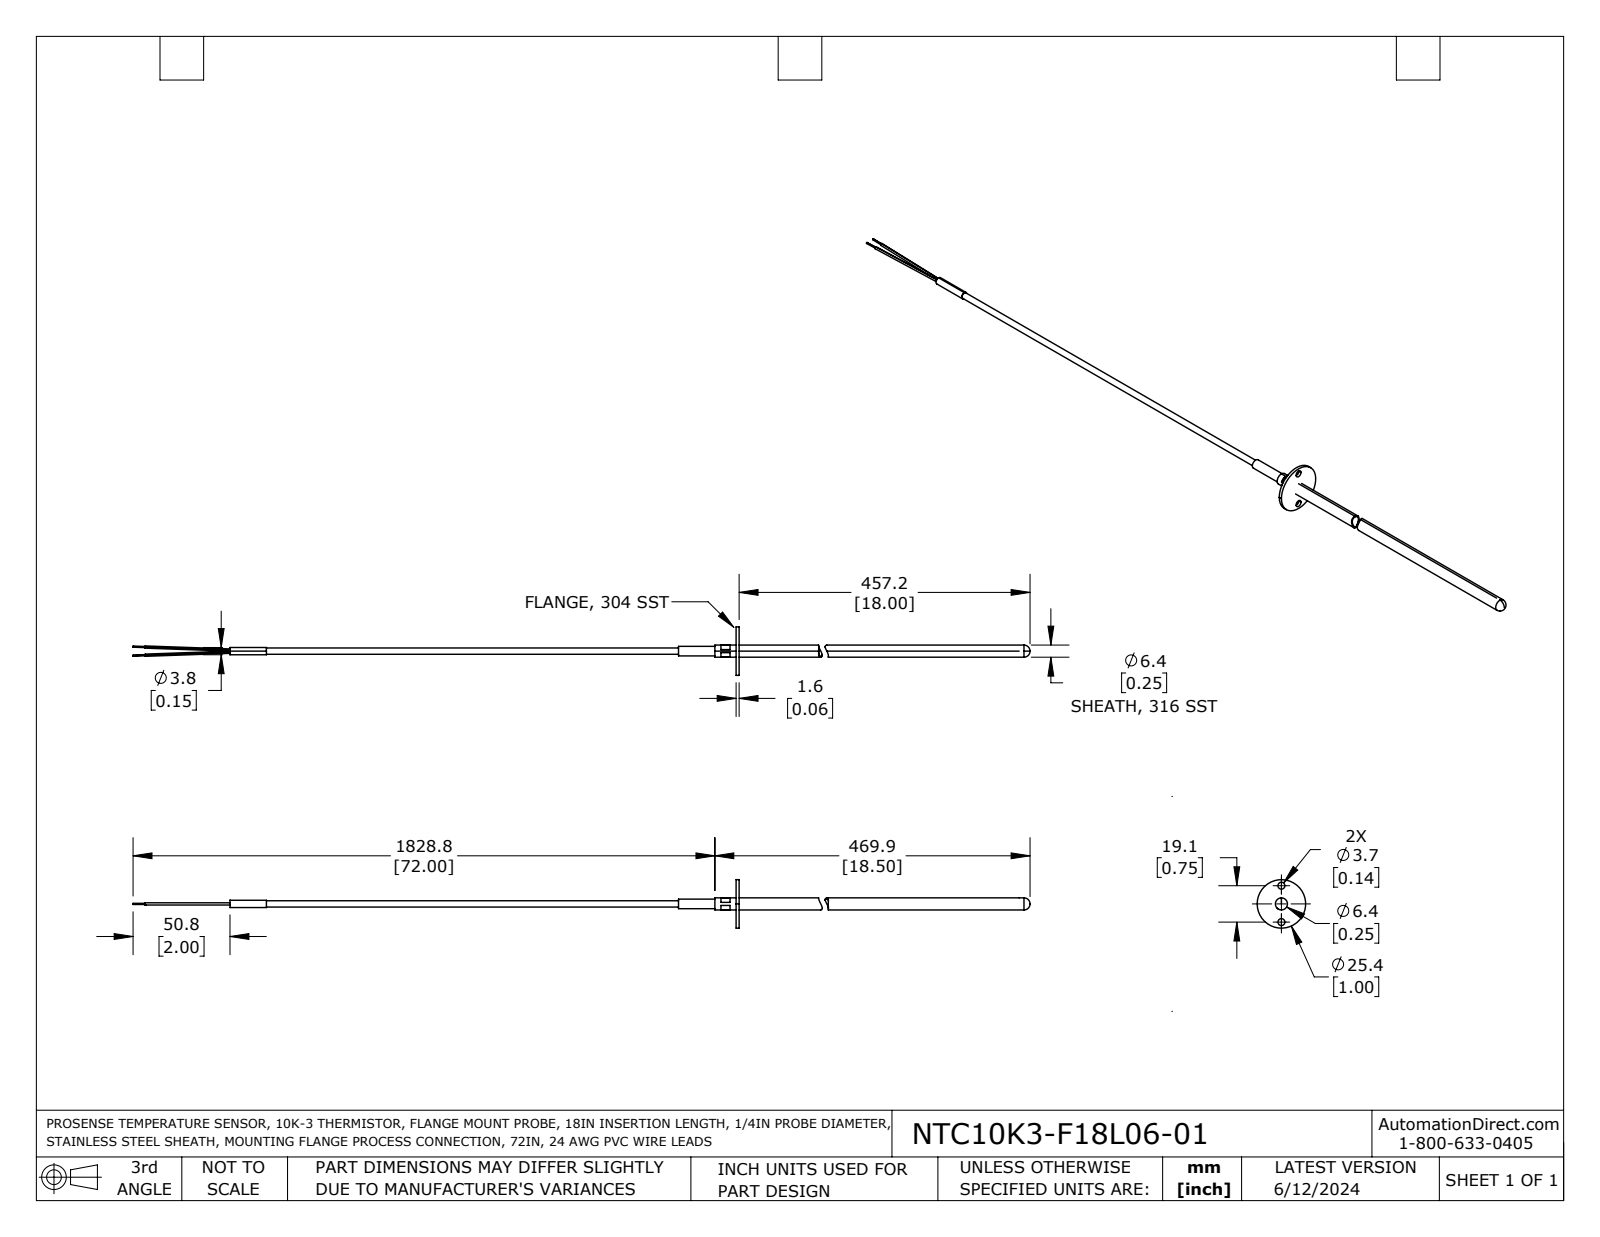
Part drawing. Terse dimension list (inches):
name: NTC10K3-F18L06-01
written by: SolidWorks 2021 (AUTOMOTIVE_DESIGN)
unit: in
bodies: 4 solids, 59 faces (27 planar, 22 cylindrical, 10 other)
size: 30.495 × 1 × 1
volume: 0.464 in³; area: 35.53 in²
holes: 2× ⌀0.144, 1× ⌀0.131, 1× ⌀0.187, 1× ⌀0.191, 1× ⌀0.21
bosses: 1× ⌀1, 1× ⌀0.25, 1× ⌀0.197, 1× ⌀0.15, 1× ⌀0.13
face distances: 0.063, 0.216, 17.838, 17.775, 0.437, 0.5, 18.275, 0.313, 10.001, 10.439
hole spacings: 0.375, 0.75
